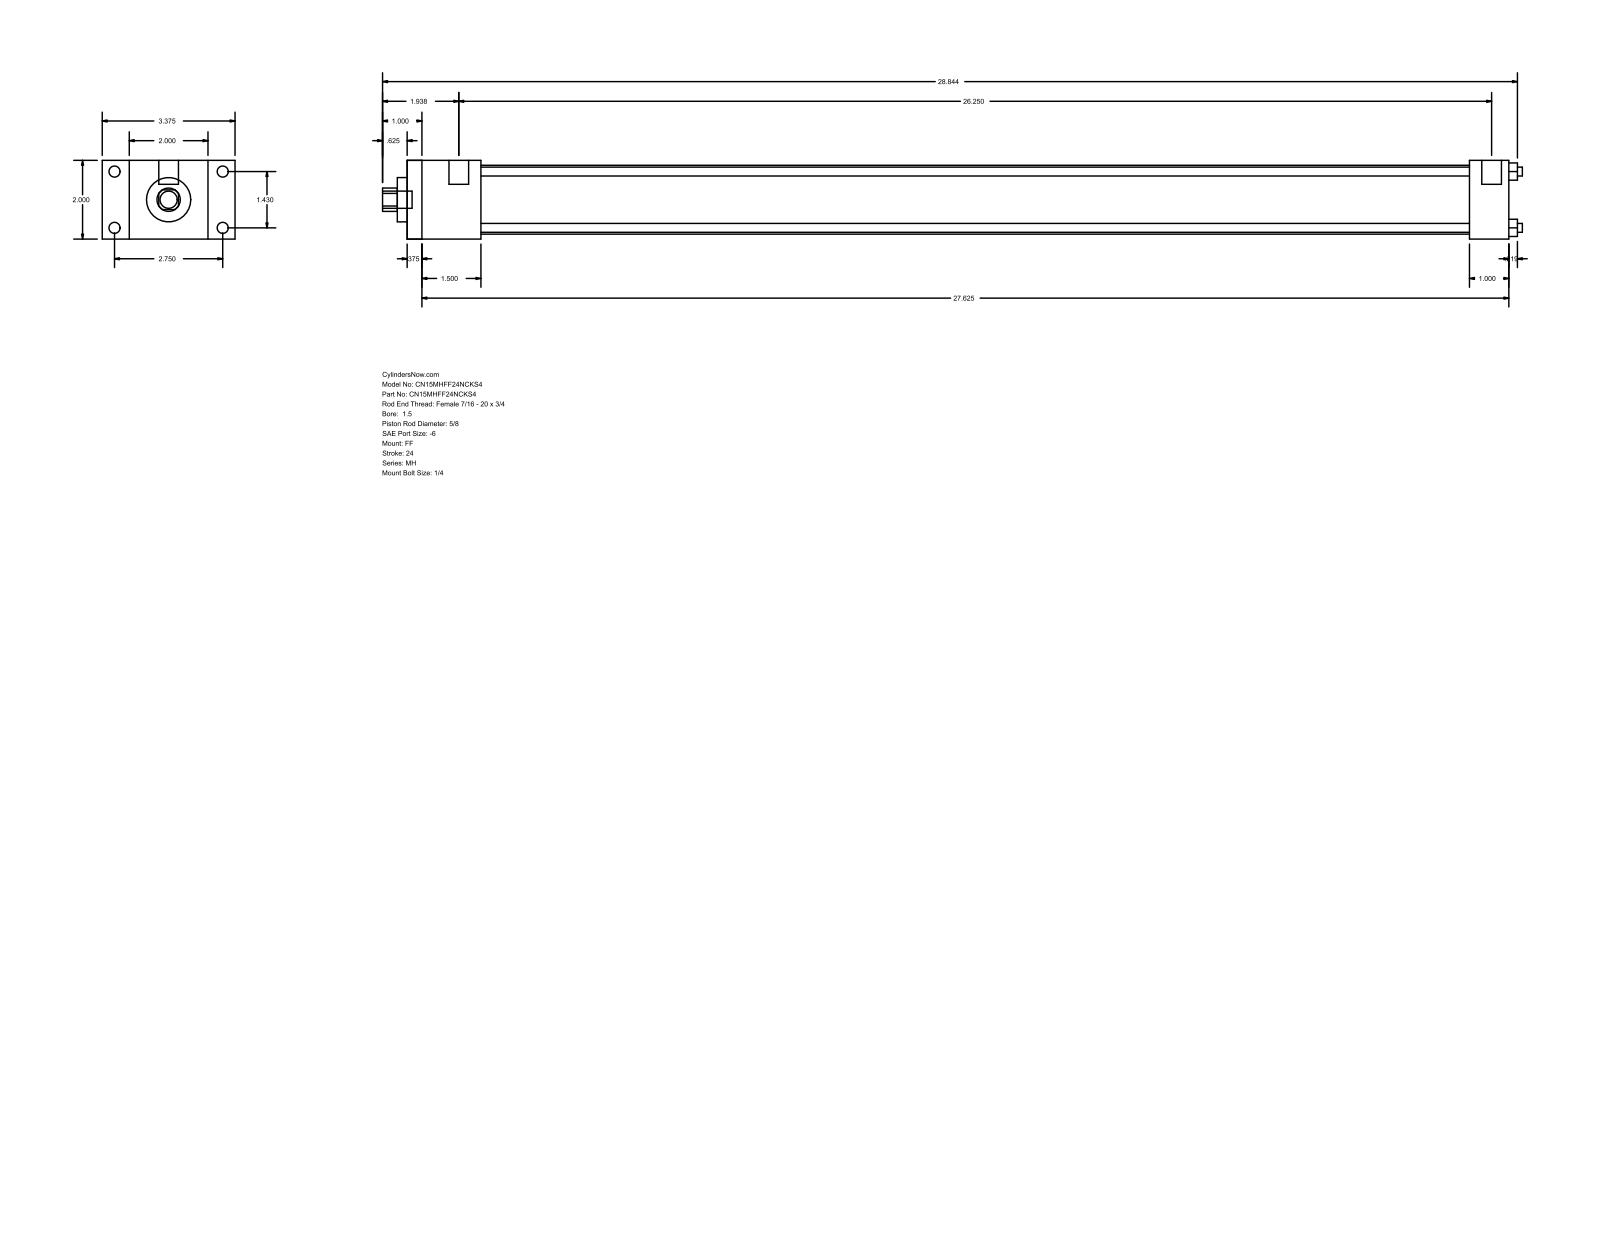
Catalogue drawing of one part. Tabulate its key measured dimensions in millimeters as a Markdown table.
| quantity | value |
| --- | --- |
| part name | MH_FF__0150_0.625 |
| STEP written by | GSSL Pune (CONFIG_CONTROL_DESIGN) |
| units | millimeters |
| bodies | 0 solids, 92 faces (64 planar, 28 cylindrical, 0 other) |
| overall size | 735.81 × 85.72 × 50.8 |
| round holes (diameter × count) | 5.71 × 4, 15.88 × 1, 28.57 × 1, 44.45 × 1 |
| round bosses / shafts (diameter × count) | 7.14 × 4, 5.56 × 4, 12.7 × 2, 11.11 × 1 |
| partial cylindrical surfaces (radius × count) | 7.54 × 1 |
| main face-to-face distances | 50.8, 711.2, 9.52, 701.68, 17.46, 68.26, 47.62, 38.1, 663.58, 685.79 |
| hole center spacings | 25.68, 36.32, 51.36 |
